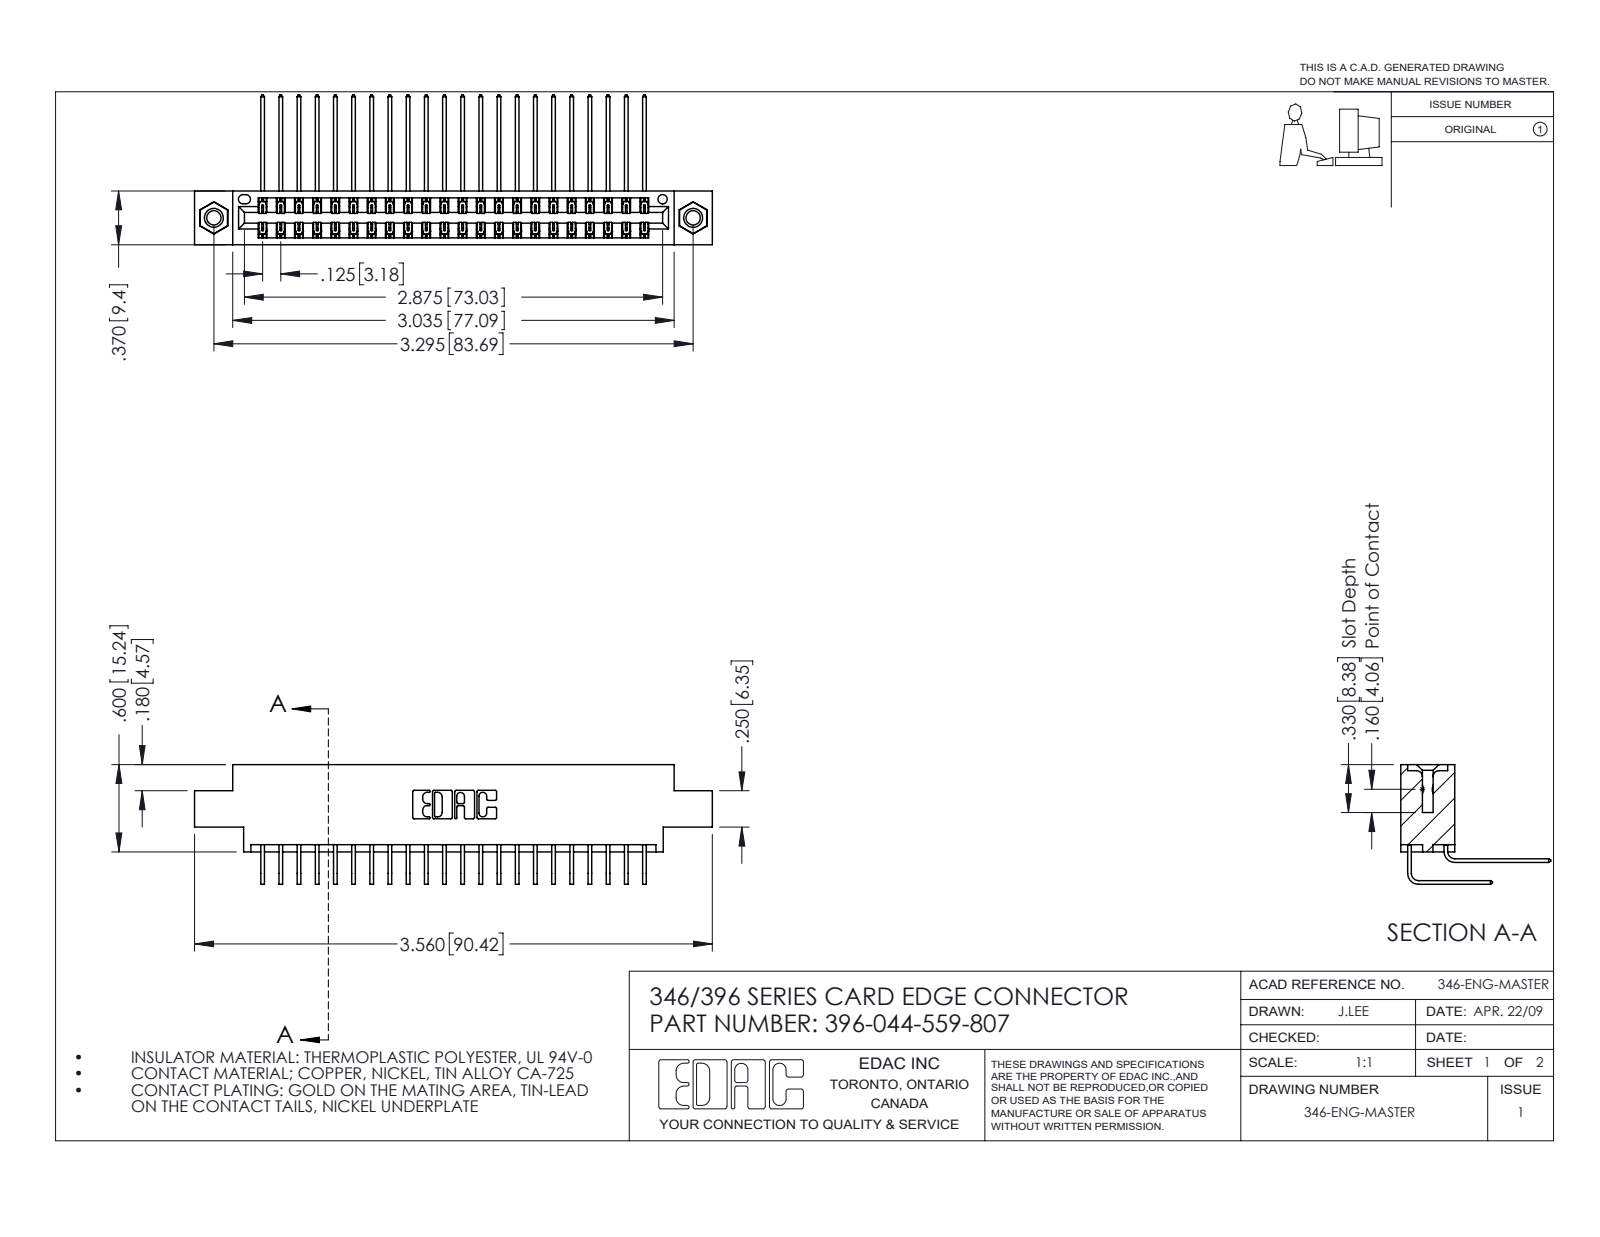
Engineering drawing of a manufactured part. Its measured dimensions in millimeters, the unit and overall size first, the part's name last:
Units: millimetres
Overall size (bounding box): 90.4 × 26.2 × 20.9
Round holes (diameter × count): ⌀2.5 ×2, ⌀3.2 ×2, ⌀4 ×2, ⌀1.6 ×1
Round bosses / shafts (diameter × count): ⌀3.9 ×2
Partial cylindrical surfaces — rounded edges, fillets, slot ends (radius × count): R0.2 ×66, R0.3 ×22, R0.2 ×6, R0.8 ×6, R0.7 ×3, R0.4 ×2, R0.6 ×2, R0.6 ×2
Main face-to-face distances: 1.2, 8.2, 0.6, 9.4, 6.4, 1.8, 7.6, 7, 5.6, 3.8
Hole centre spacings: 6.2, 78.4, 83.7
Volume: 8 750 mm³ · Surface area: 13 140 mm²
Bodies: 47 solids, 2562 faces (1740 planar, 806 cylindrical, 16 other)
Part name (STEP PRODUCT): 396-044-559-807; 345-292-001_558 559 Tail - 1; 345-250-001_345-250-005-103; 345-292-001_559 Tail - 2 (+1 more)
STEP written by: SolidWorks 2016 (CONFIG_CONTROL_DESIGN)
